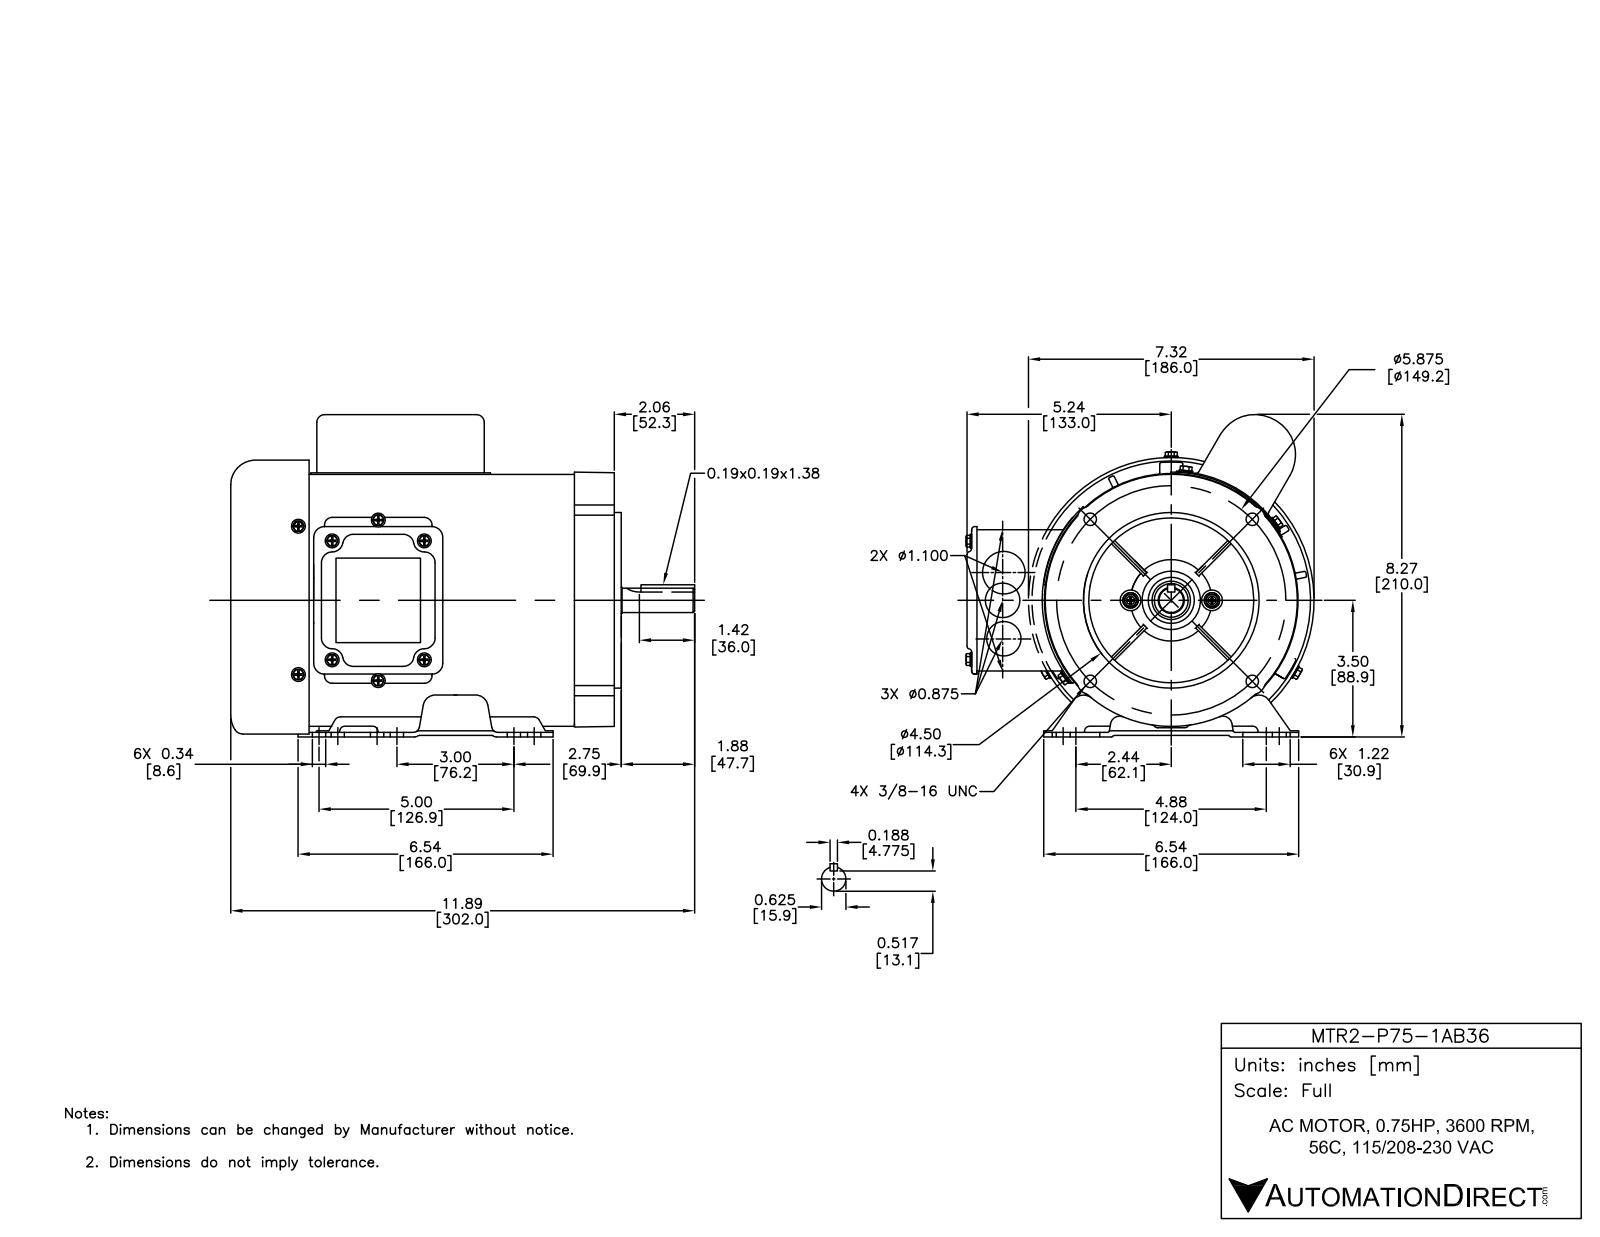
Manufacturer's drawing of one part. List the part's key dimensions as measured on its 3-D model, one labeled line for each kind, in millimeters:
Part name (STEP PRODUCT): Front keyed shaft; Fan Guard A; Tail Shaft A; Shaft A (+8 more)
STEP written by: SolidWorks 2015 (AUTOMOTIVE_DESIGN)
Units: millimetres
Bodies: 54 solids, 2470 faces (932 planar, 1010 cylindrical, 528 other)
Overall size (bounding box): 301.9 × 255.3 × 246.6
Volume: 878 300 mm³ · Surface area: 709 000 mm²
Round holes (diameter × count): ⌀5.6 ×13, ⌀5 ×12, ⌀7 ×8, ⌀5.5 ×6, ⌀6.3 ×6, ⌀8.7 ×6, ⌀3.5 ×5, ⌀3.9 ×4, ⌀8 ×4, ⌀18 ×3, ⌀3.3 ×2, ⌀3.4 ×2
Round bosses / shafts (diameter × count): ⌀8.8 ×13, ⌀4.2 ×13, ⌀6.3 ×4, ⌀14 ×2, ⌀10.5 ×2, ⌀4.8 ×2, ⌀182.5 ×1, ⌀165 ×1
Partial cylindrical surfaces — rounded edges, fillets, slot ends (radius × count): R3 ×101, R1 ×66, R5.8 ×24, R1.9 ×23, R5 ×22, R7 ×17, R2.5 ×16, R3 ×14
Main face-to-face distances: 1, 6, 3, 1.9, 1.6, 213, 35.6, 41.6, 34.6, 40.6
Hole centre spacings: 77, 60, 107.2, 97.6, 2.4, 74.6, 95.2, 105.5
